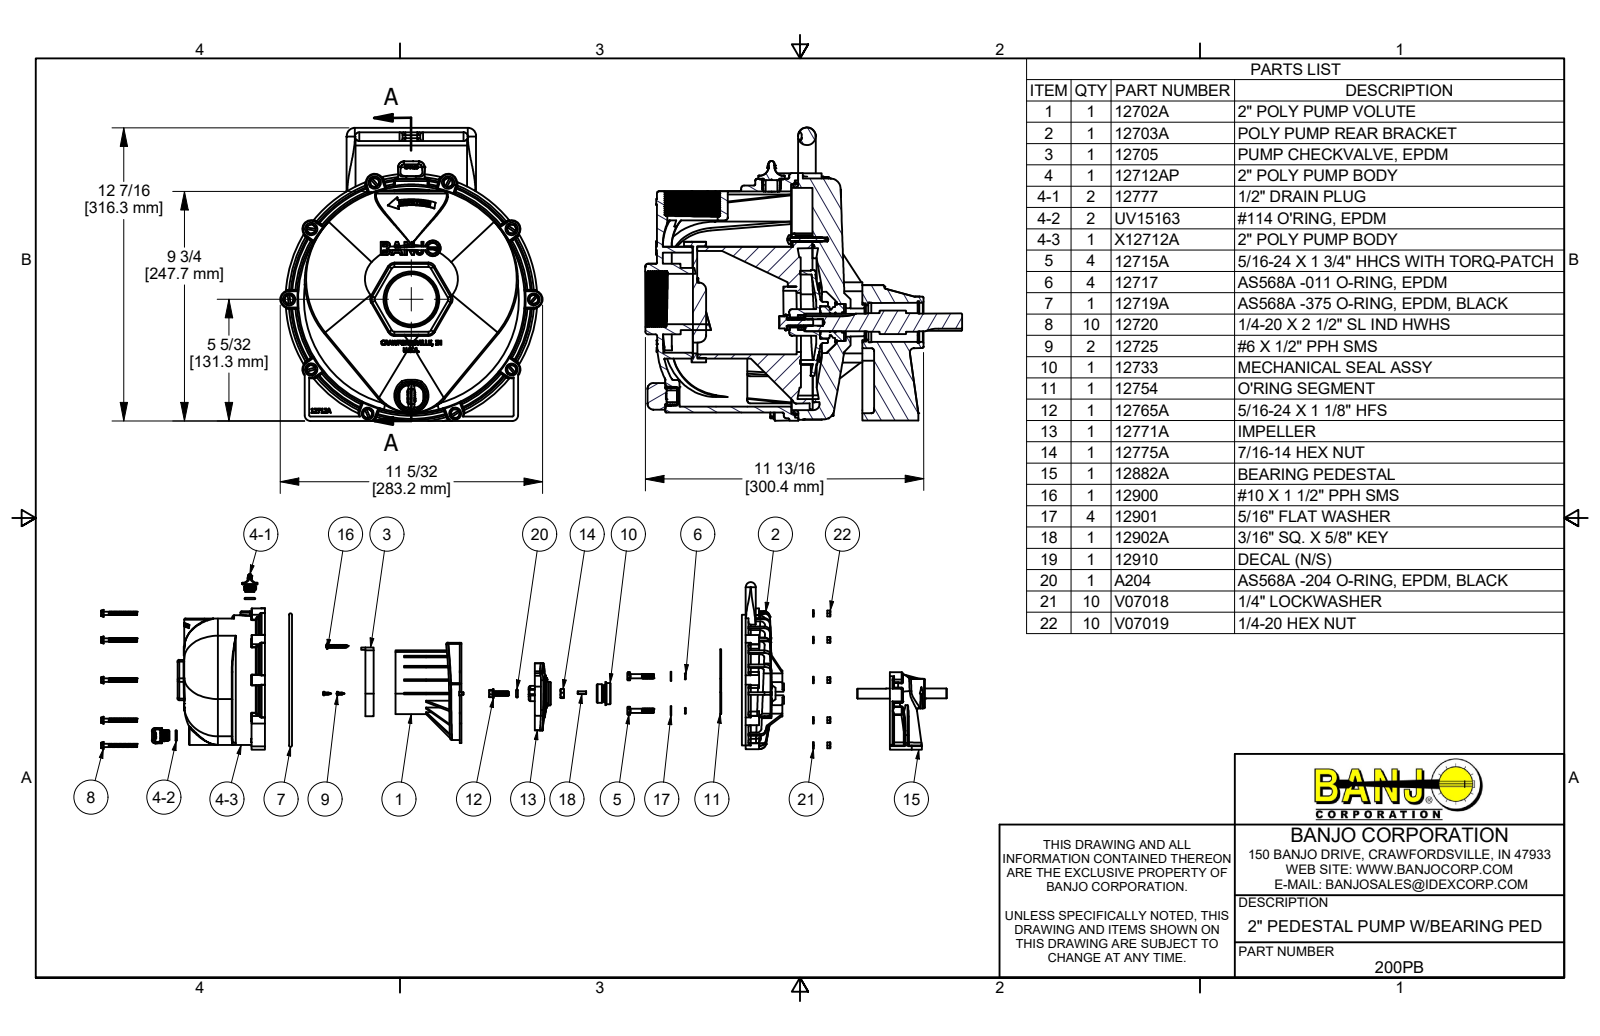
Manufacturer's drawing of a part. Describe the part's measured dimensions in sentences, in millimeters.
The part is named "200PB; 12703A; 12712AP; X12712A (+8 more)". Its 3-D file was written by "Autodesk Inventor 2019 (AUTOMOTIVE_DESIGN)". It is 86 solids with 8080 faces: 2203 planar, 2231 cylindrical and 3646 other. Overall it measures 351.1 by 341.9 by 283.2 millimeters. Its volume is 3 181 000 cubic millimeters and its surface area 1 226 000 square millimeters. Round holes: 10 of diameter 5, 10 of diameter 6.4, 10 of diameter 6.9, 7 of diameter 5.6, 5 of diameter 6.8, 4 of diameter 8.7, 4 of diameter 10.3, 4 of diameter 11.9, 4 of diameter 20.7, 2 of diameter 2, 2 of diameter 2.9, 2 of diameter 2.9. Round bosses or shafts: 80 of diameter 7, 10 of diameter 13.2, 10 of diameter 12.4, 10 of diameter 6.4, 6 of diameter 4.9, 4 of diameter 17.5, 4 of diameter 8, 3 of diameter 28.7. Partial cylindrical surfaces (rounded edges, fillets, slot ends): 116 of radius 0.8, 77 of radius 1.5, 35 of radius 6.4, 31 of radius 3.2, 26 of radius 0.2, 24 of radius 4.7, 13 of radius 0.4, 13 of radius 9.5. The main face-to-face distances are 4.6, 5.1, 25.4, 0.9, 4.1, 6.4, 73.2, 2.8, 3.2, 12.7. The hole center spacings are 132.1, 46, 65, 79.5, 156.2, 213, 264.2, 33.3.
